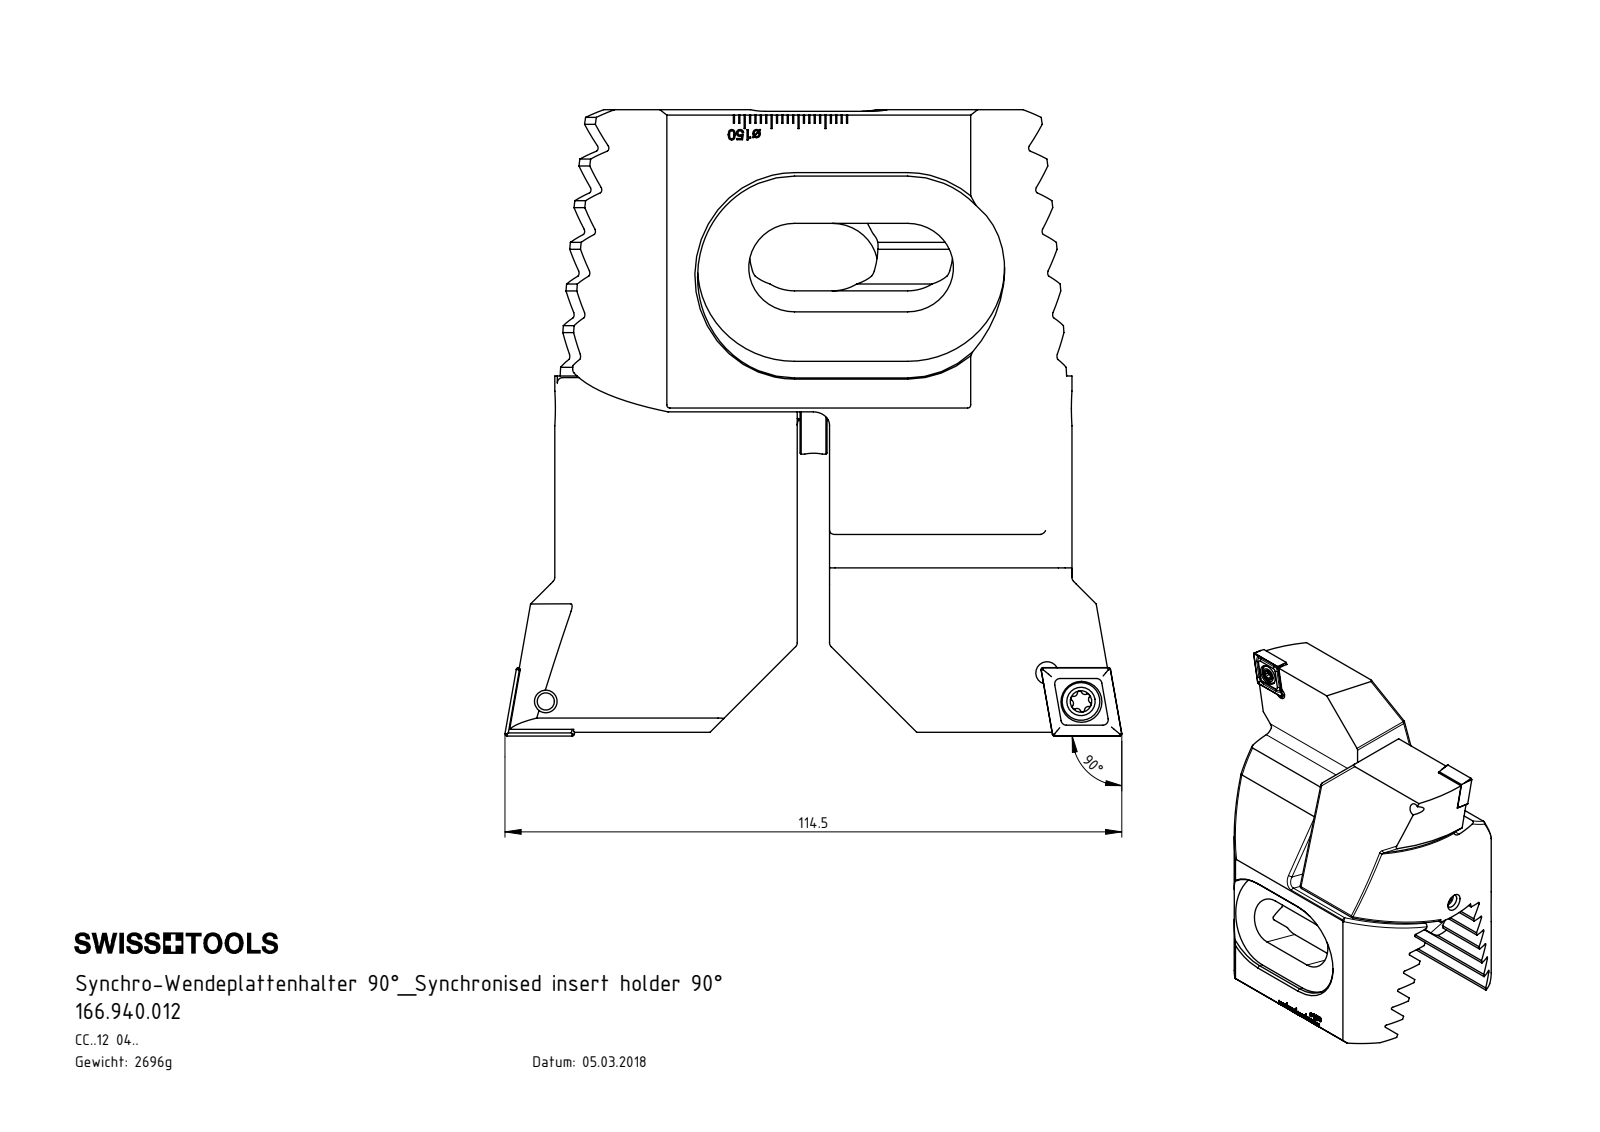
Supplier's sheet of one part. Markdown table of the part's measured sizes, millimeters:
| quantity | value |
| --- | --- |
| part name | Z42-ER3.002.005_A; ISO 4026 - M4 x 5; CCMT120404; Z94-xxx.001.067_E (+4 more) |
| STEP written by | SolidWorks 2017 (CONFIG_CONTROL_DESIGN) |
| units | millimeters |
| bodies | 11 solids, 853 faces (469 planar, 154 cylindrical, 230 other) |
| overall size | 115.5 × 114.5 × 75.2 |
| volume | 343 499 mm³ |
| surface area | 65 522 mm² |
| round holes (diameter × count) | 4.2 × 4, 3.3 × 3, 2 × 2, 5.5 × 2, 7.6 × 2, 5 × 1 |
| round bosses / shafts (diameter × count) | 4 × 3, 7 × 2, 5 × 2, 17 × 1, 6 × 1, 3.8 × 1 |
| partial cylindrical surfaces (radius × count) | 1 × 16, 0.39 × 12, 0.58 × 12, 0.69 × 8, 3 × 6, 0.69 × 4, 8.5 × 4, 12 × 4 |
| main face-to-face distances | 6.93, 20.78, 27.71, 13.85, 13.86, 13.19, 37.3, 37.9, 6.92, 1.59 |
| hole center spacings | 8.21, 8.33, 25, 93.2, 93.29, 99.43, 48.3, 86.76 |
